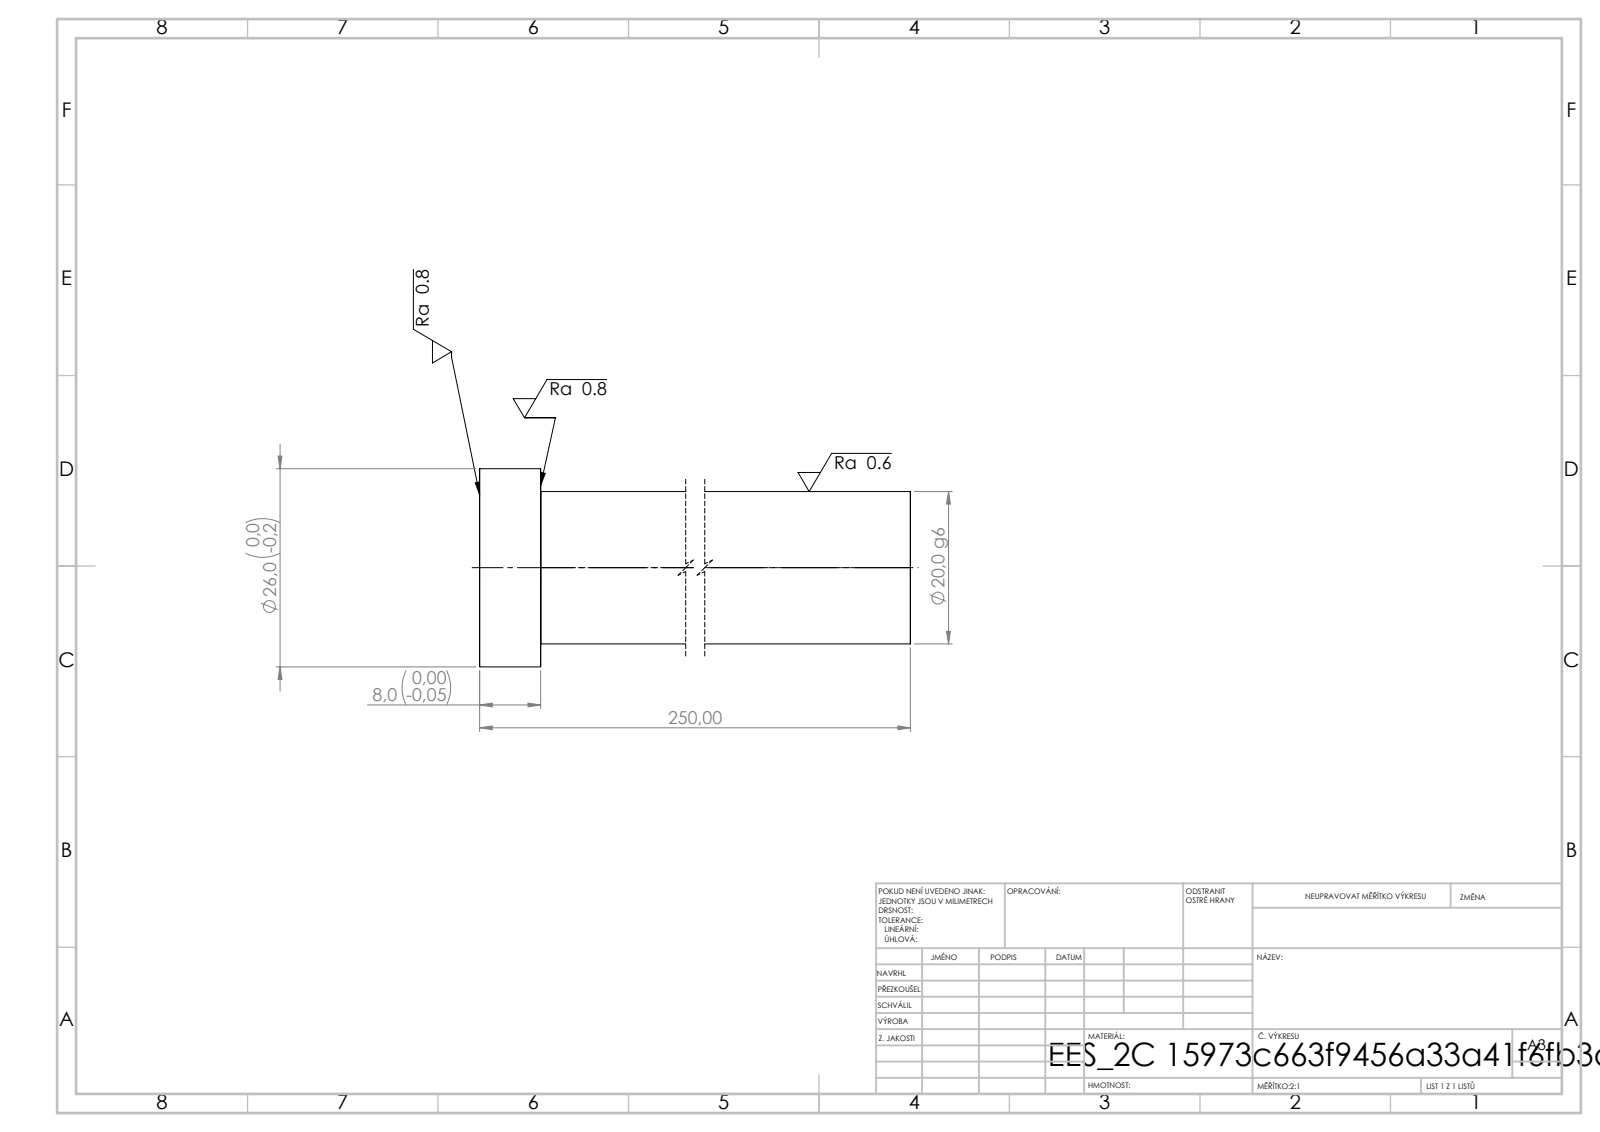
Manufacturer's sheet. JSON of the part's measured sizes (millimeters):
{"step_written_by": "SolidWorks 2019 (CONFIG_CONTROL_DESIGN)", "units": "millimeters", "bodies": {"solids": 1, "faces": 7, "planar": 3, "cylindrical": 4, "other": 0}, "overall_size": [250, 26, 26], "volume_mm3": 80274, "surface_area_mm2": 16921, "round_bosses_or_shafts": [[26, 1], [20, 1]], "face_to_face_distances": [250, 8, 242]}
